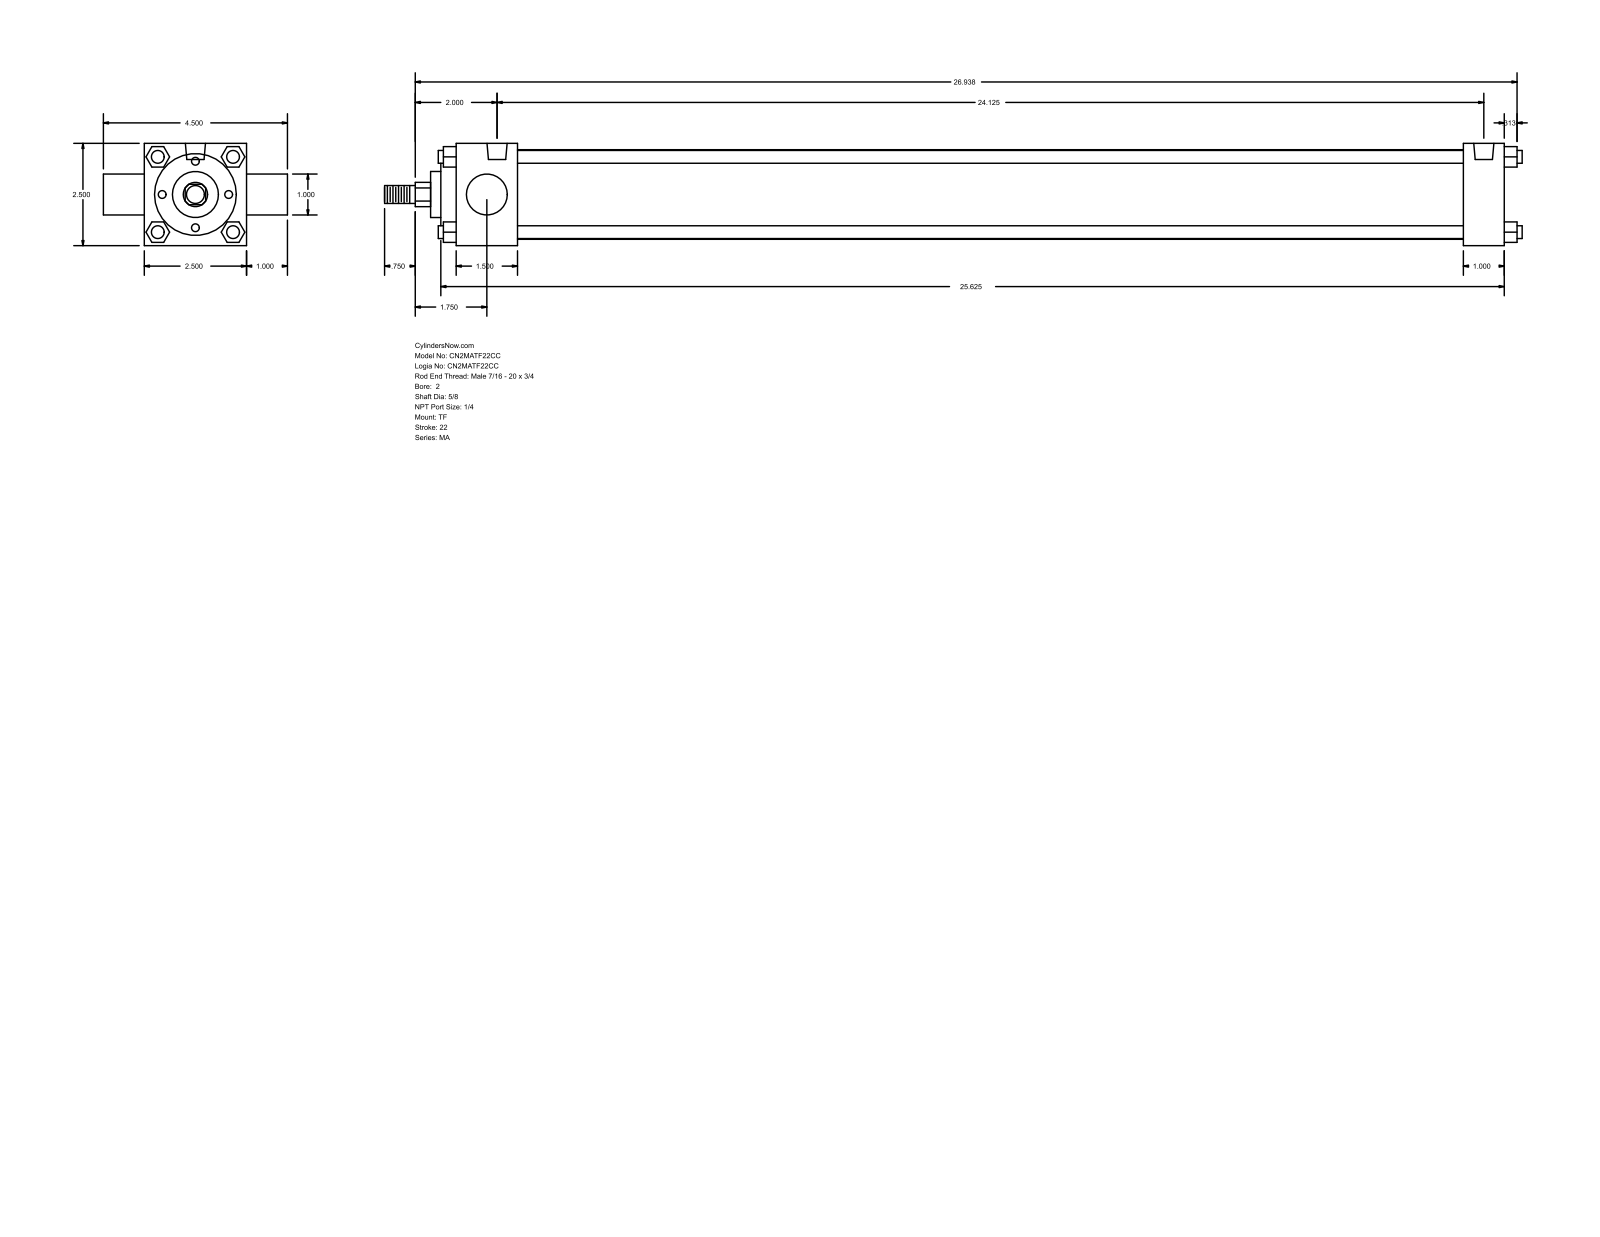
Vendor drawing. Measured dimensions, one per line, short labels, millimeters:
name: MA_TF__0200_0.625
written by: GSSL Pune (CONFIG_CONTROL_DESIGN)
unit: mm
bodies: 0 solids, 122 faces (93 planar, 29 cylindrical, 0 other)
size: 706.44 × 114.3 × 63.5
holes: 3× ⌀7.94, 2× ⌀12.49
bosses: 4× ⌀7.94, 1× ⌀55.63, 1× ⌀50.8, 1× ⌀28.57, 1× ⌀25.4, 1× ⌀15.88, 1× ⌀11.11
rounds: 1× R7.54
face distances: 63.5, 38.1, 12.7, 650.87, 625.48, 587.38, 612.77, 25.39, 9.52, 47.62
hole spacings: 612.78
